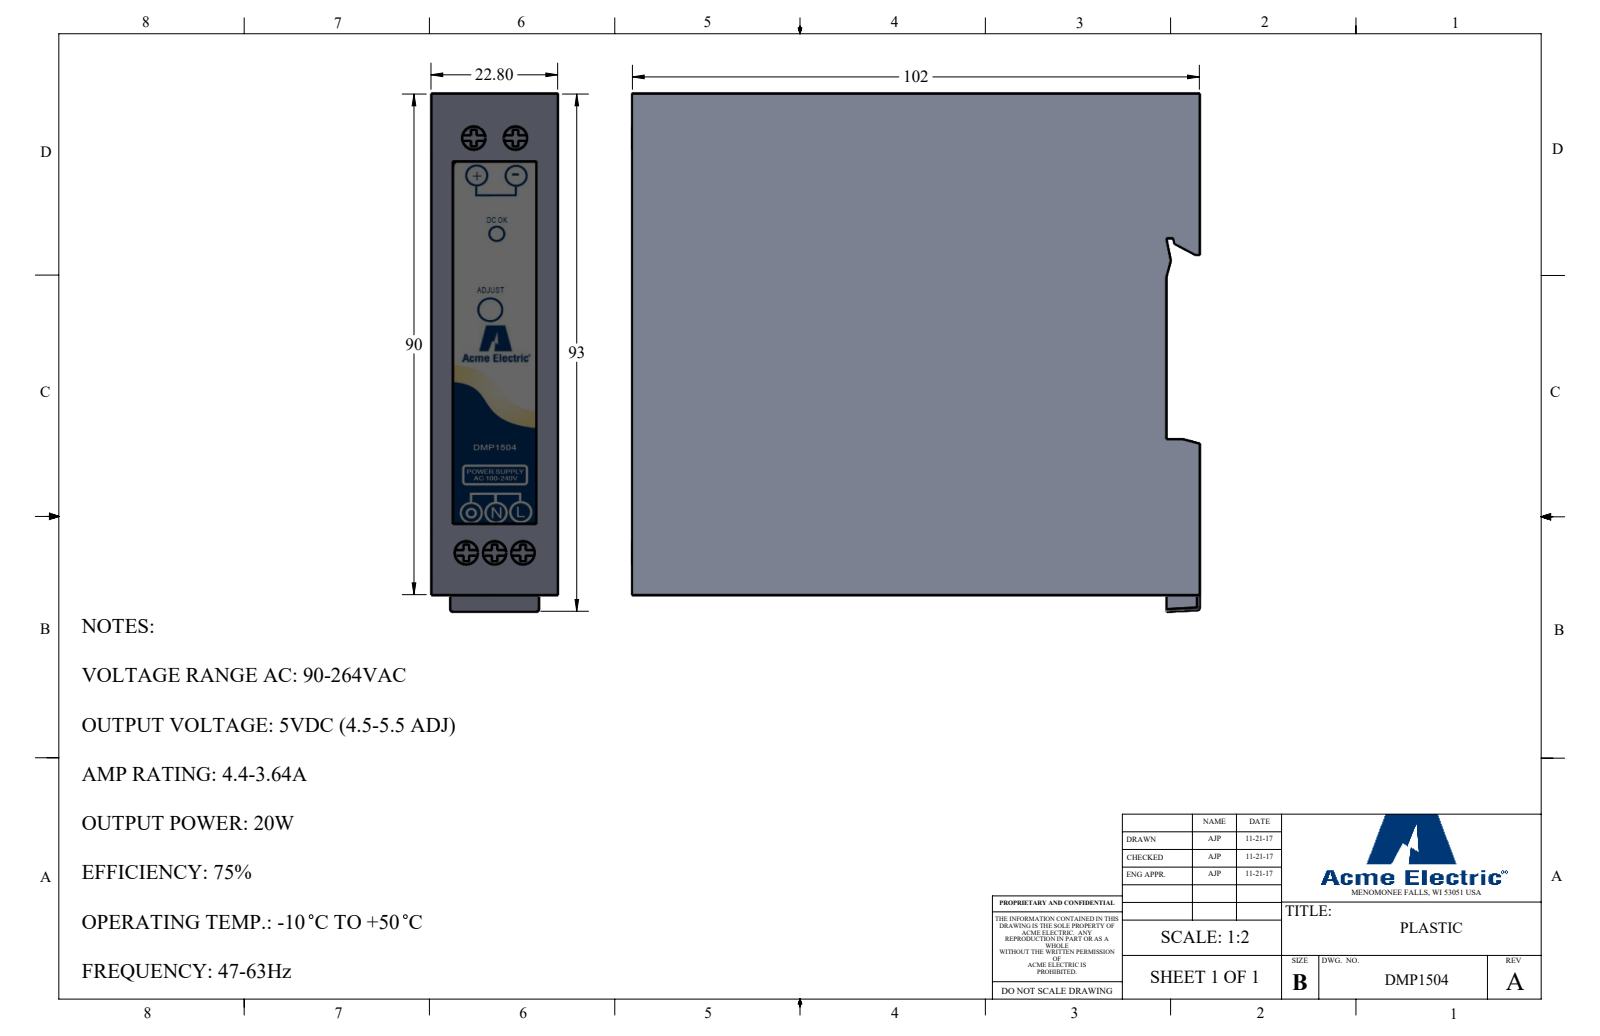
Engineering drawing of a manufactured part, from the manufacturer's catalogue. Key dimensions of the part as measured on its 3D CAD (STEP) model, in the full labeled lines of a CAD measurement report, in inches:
Part name (STEP PRODUCT): DMP1504
STEP written by: SolidWorks 2017 (AUTOMOTIVE_DESIGN)
Units: inches
Bodies: 1 solid, 103 faces (86 planar, 15 cylindrical, 2 other)
Overall size (bounding box): 4.016 × 3.661 × 0.898
Volume: 12.5 in³ · Surface area: 42.27 in²
Round holes (diameter × count): ⌀0.165 ×5
Partial cylindrical surfaces — rounded edges, fillets, slot ends (radius × count): R0.02 ×5
Main face-to-face distances: 0.898, 3.543, 4.016, 0.236, 3.78, 1.102, 2.441, 0.039, 3.976, 3.74
Hole centre spacings: 0.201, 2.93, 2.933, 2.95, 0.295, 0.402
